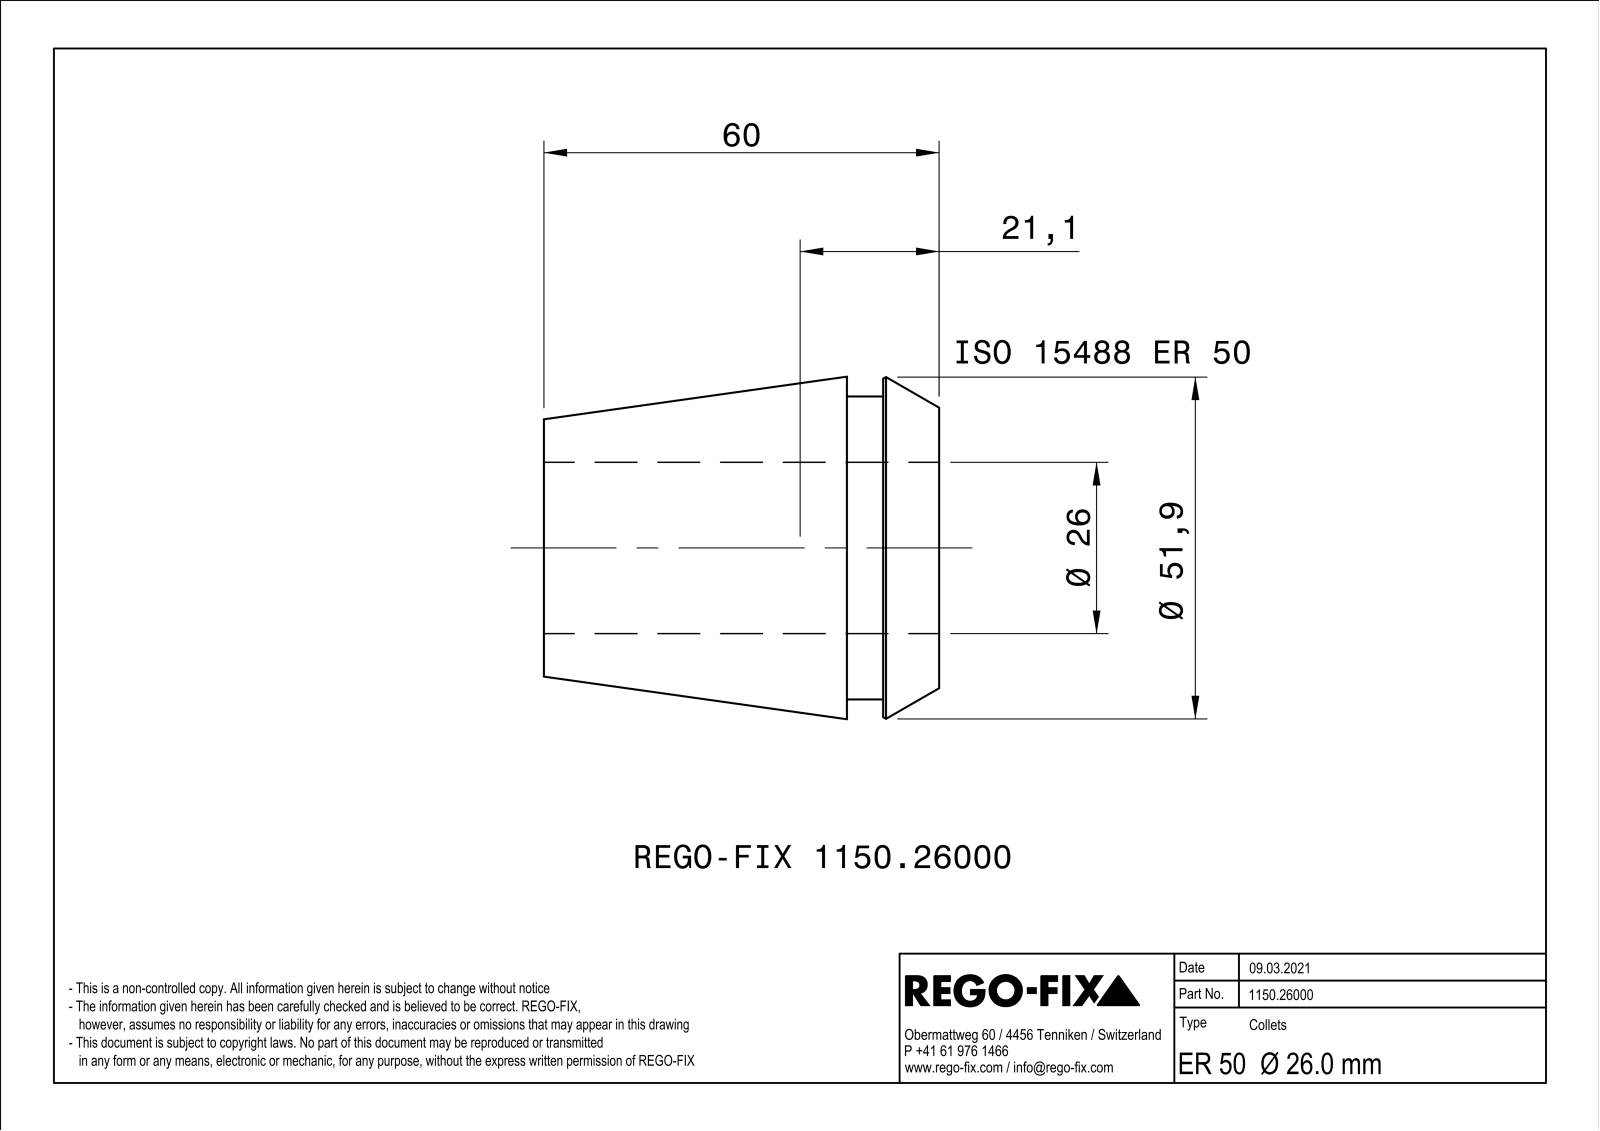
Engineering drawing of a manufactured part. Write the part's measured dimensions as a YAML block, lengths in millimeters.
part_name: "NOCUT"
step_written_by: "SIEMENS PLM Software Solid Edge ST10 (AUTOMOTIVE_DESIGN)"
units: millimeters
bodies: {solids: 1, faces: 177, planar: 88, cylindrical: 9, other: 80}
overall_size: [60, 51.99, 51.99]
volume: 59248
surface_area: 31468
round_holes:
  - {diameter: 26, count: 1}
round_bosses_or_shafts:
  - {diameter: 46, count: 1}
face_to_face_distances: [1, 60, 14, 46, 8.5, 5.5, 51.5, 9, 0.5, 5]
